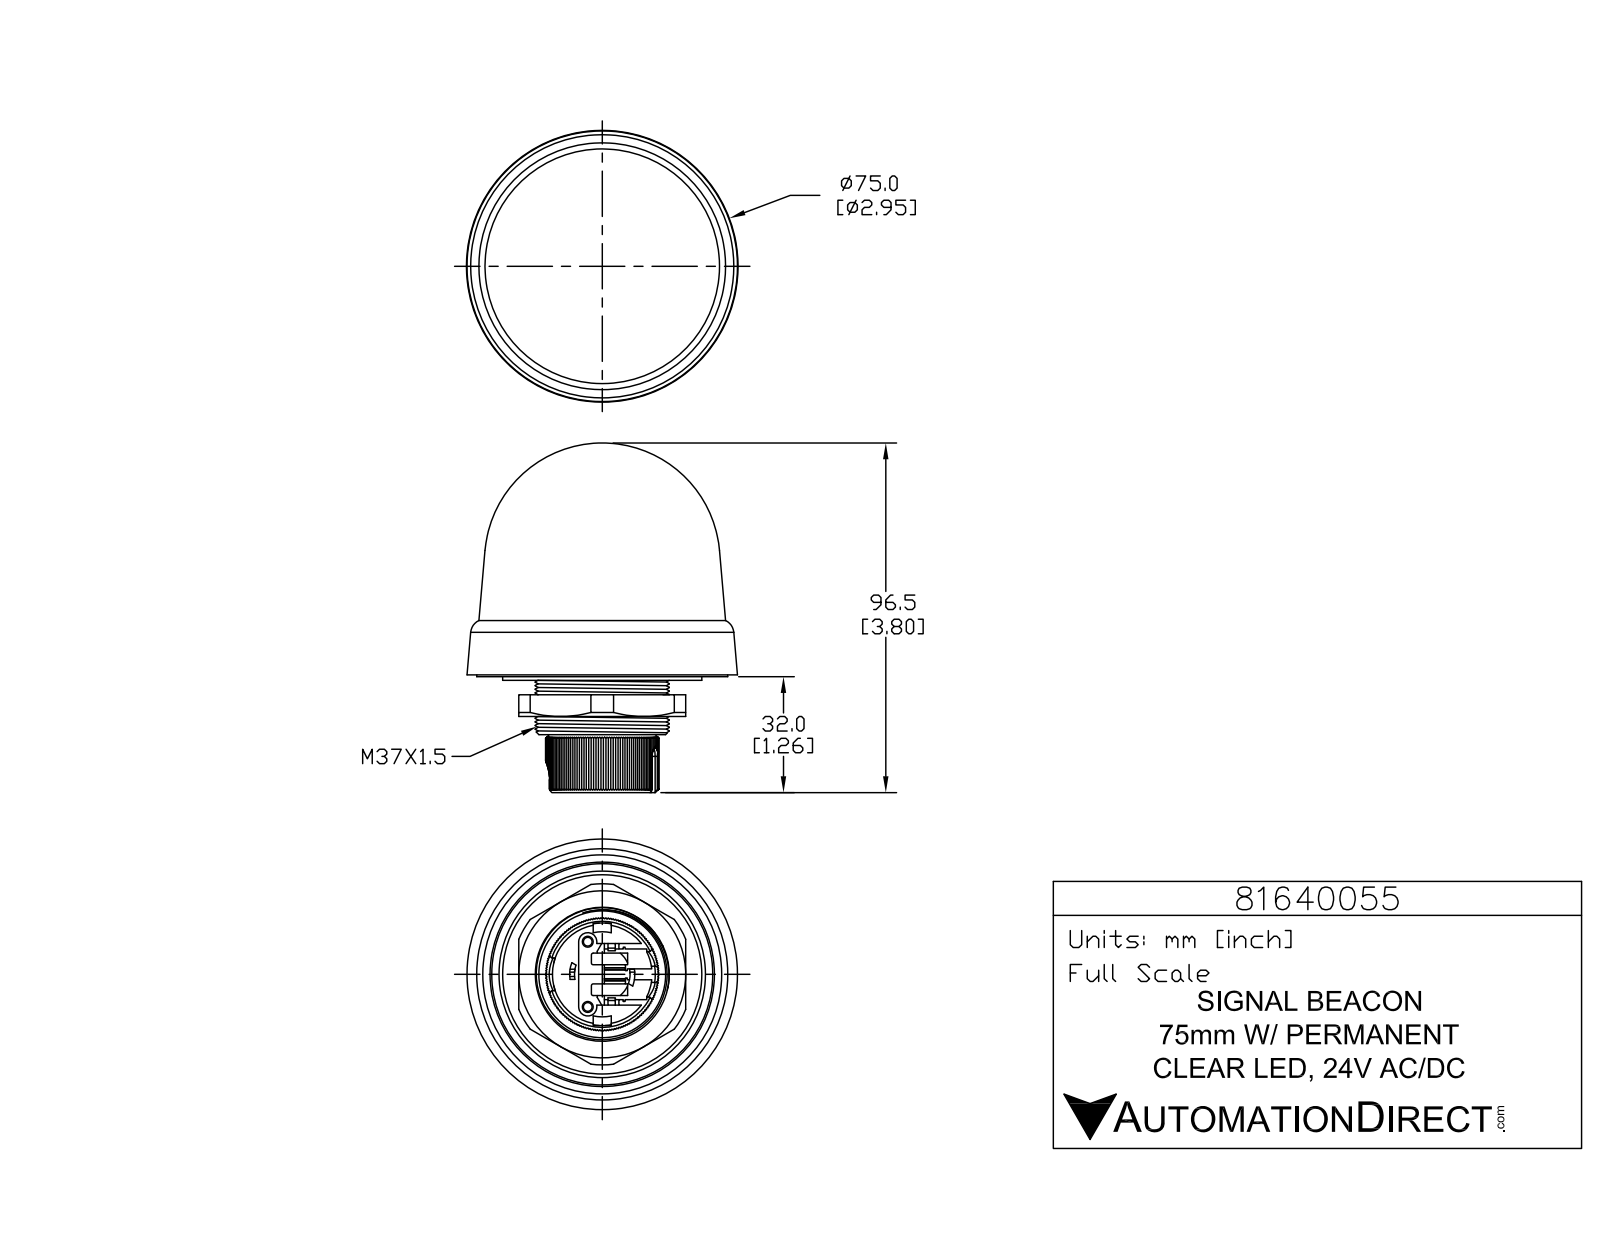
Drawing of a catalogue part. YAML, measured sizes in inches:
part_name: "81640055"
step_written_by: "SolidWorks 2019 (CONFIG_CONTROL_DESIGN)"
units: inches
bodies: {solids: 3, faces: 560, planar: 432, cylindrical: 80, other: 48}
overall_size: [3.799, 2.941, 2.941]
volume: 12.36
surface_area: 58.68
round_holes:
  - {diameter: 0.094, count: 2}
  - {diameter: 0.118, count: 2}
  - {diameter: 0.604, count: 1}
  - {diameter: 1.142, count: 1}
round_bosses_or_shafts:
  - {diameter: 0.217, count: 2}
  - {diameter: 0.067, count: 2}
  - {diameter: 2.165, count: 1}
  - {diameter: 1.457, count: 1}
  - {diameter: 0.925, count: 1}
partial_cylinders:
  - {radius: 0.008, count: 6}
  - {radius: 0.039, count: 6}
  - {radius: 0.02, count: 4}
  - {radius: 0.031, count: 2}
  - {radius: 0.079, count: 2}
  - {radius: 0.098, count: 2}
  - {radius: 0.177, count: 1}
  - {radius: 0.354, count: 1}
face_to_face_distances: [0.177, 0.354, 0.197, 0.433, 0.512, 0.335, 0.059, 0.394, 0.118, 0.157]
hole_center_spacings: [0.388, 0.709]
